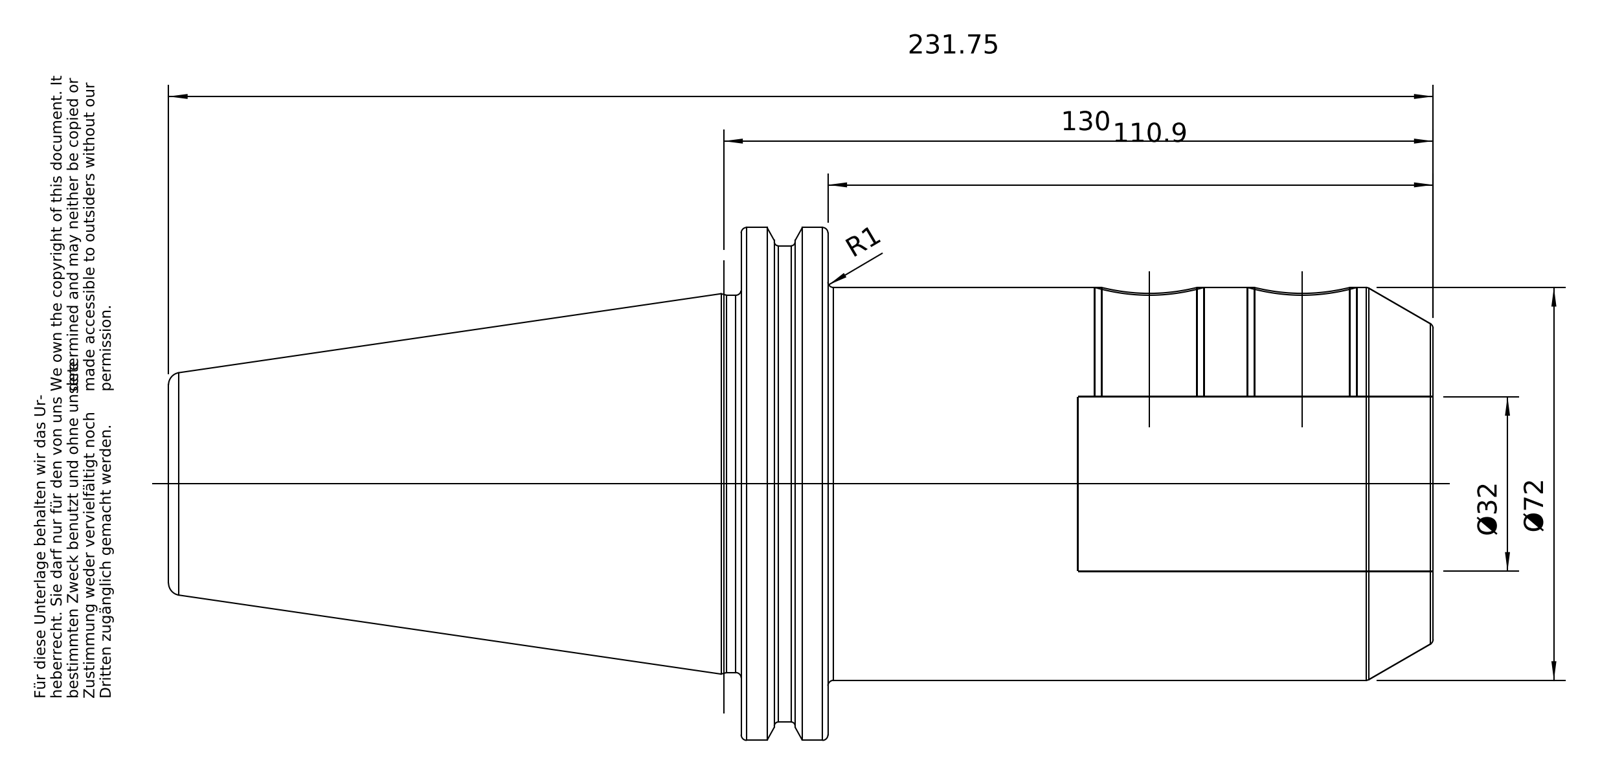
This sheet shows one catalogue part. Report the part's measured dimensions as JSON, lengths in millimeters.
{"part_name": "50-304-32", "step_written_by": "PRO/ENGINEER BY PARAMETRIC TECHNOLOGY CORPORATION, 2010430 (CONFIG_CONTROL_DESIGN)", "units": "millimeters", "bodies": {"solids": 1, "faces": 107, "planar": 22, "cylindrical": 36, "other": 49}, "overall_size": [231.6, 97.47, 94], "volume_mm3": 720110, "surface_area_mm2": 76775, "round_holes": [[17.5, 2], [20, 2], [20.75, 1], [25.01, 1], [25.7, 1], [32, 1]], "round_bosses_or_shafts": [[91, 1], [72, 1], [69.15, 1], [24.01, 1]], "partial_cylinders_radius": [[1.75, 5], [48.74, 1]], "face_to_face_distances": [15.85, 126.8, 110.95, 61.7, 45.85, 65.1, 104.8, 120.65, 166.5, 231.6], "hole_center_spacings": [28]}
